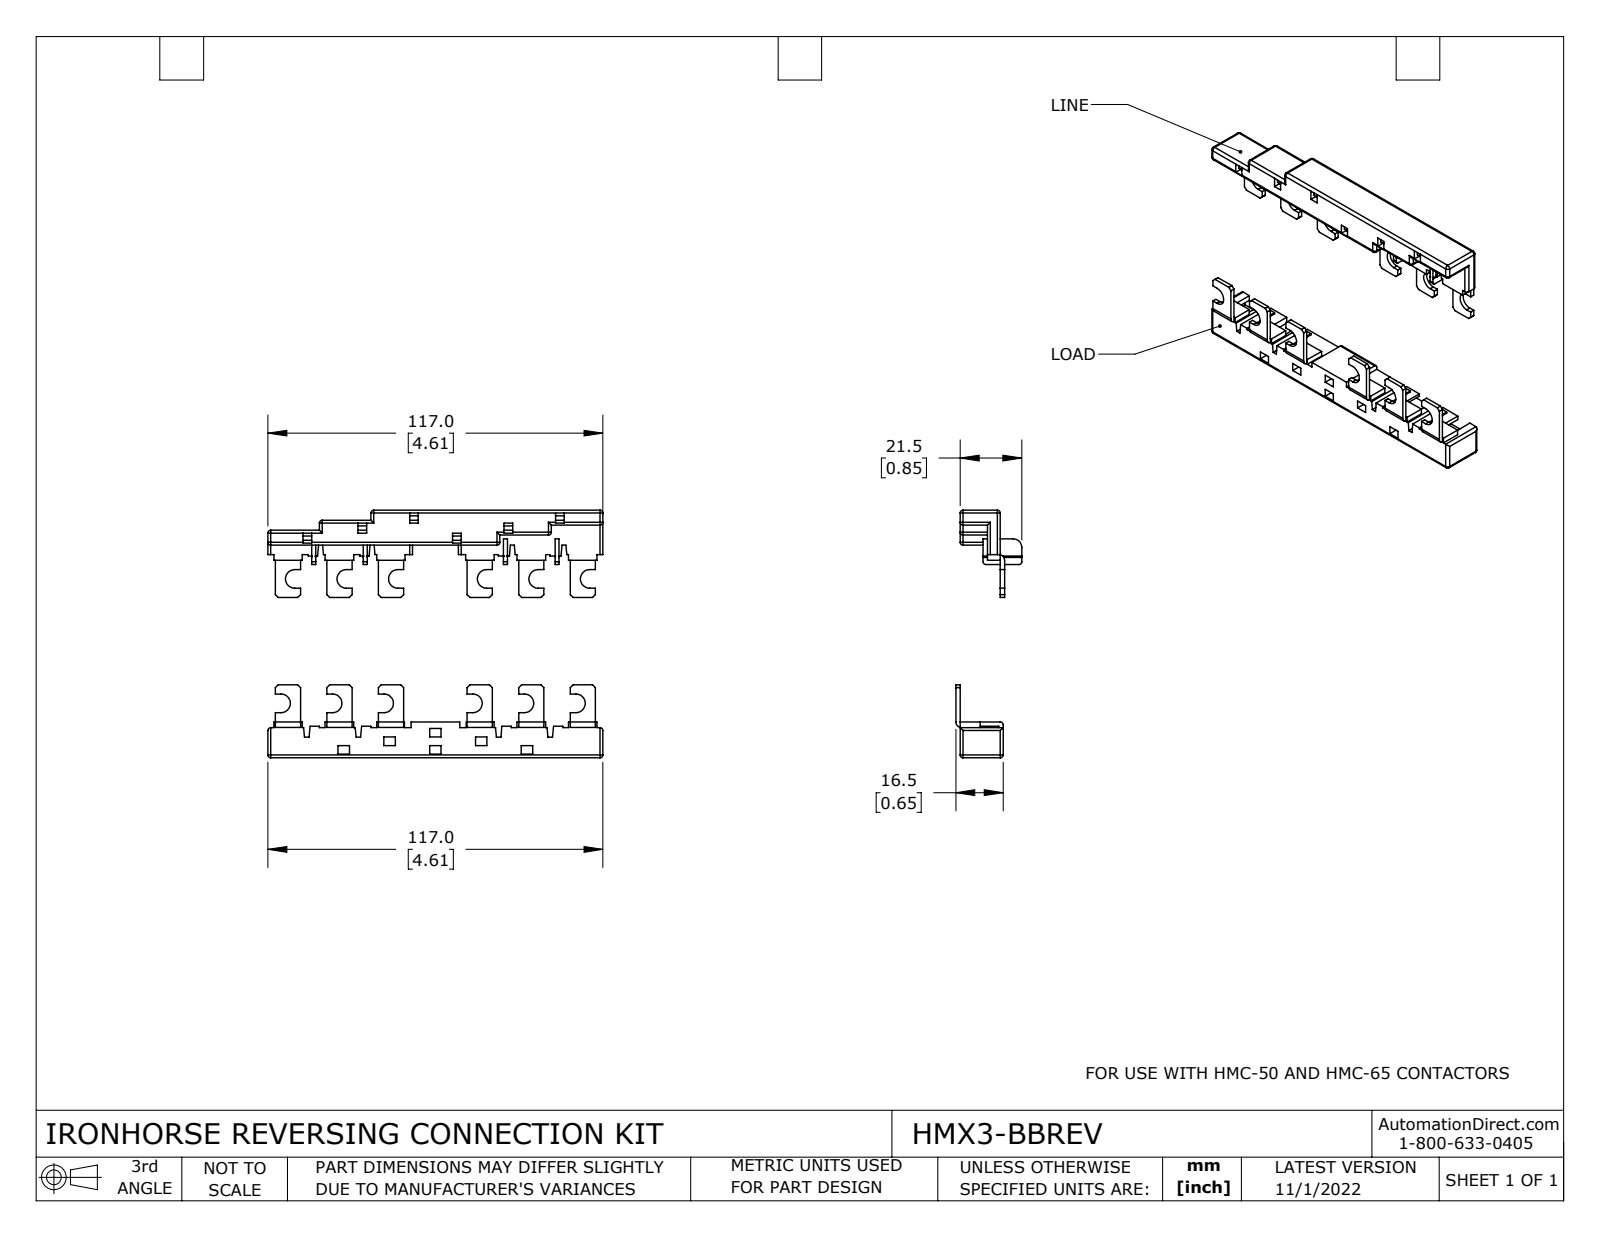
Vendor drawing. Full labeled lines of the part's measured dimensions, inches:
Part name (STEP PRODUCT): HMX3-BBREV-LINE; HMX3-BBREV; HMX3-BBREV-LOAD
STEP written by: SolidWorks 2021 (CONFIG_CONTROL_DESIGN)
Units: inches
Bodies: 2 solids, 653 faces (556 planar, 81 cylindrical, 16 other)
Overall size (bounding box): 4.606 × 3.402 × 0.906
Volume: 2.233 in³ · Surface area: 30.95 in²
Partial cylindrical surfaces — rounded edges, fillets, slot ends (radius × count): R0.039 ×45, R0.128 ×12, R0.079 ×2, R0.118 ×1
Main face-to-face distances: 0.551, 0.059, 0.217, 0.177, 0.039, 0.61, 0.276, 0.413, 3.402, 2.91
